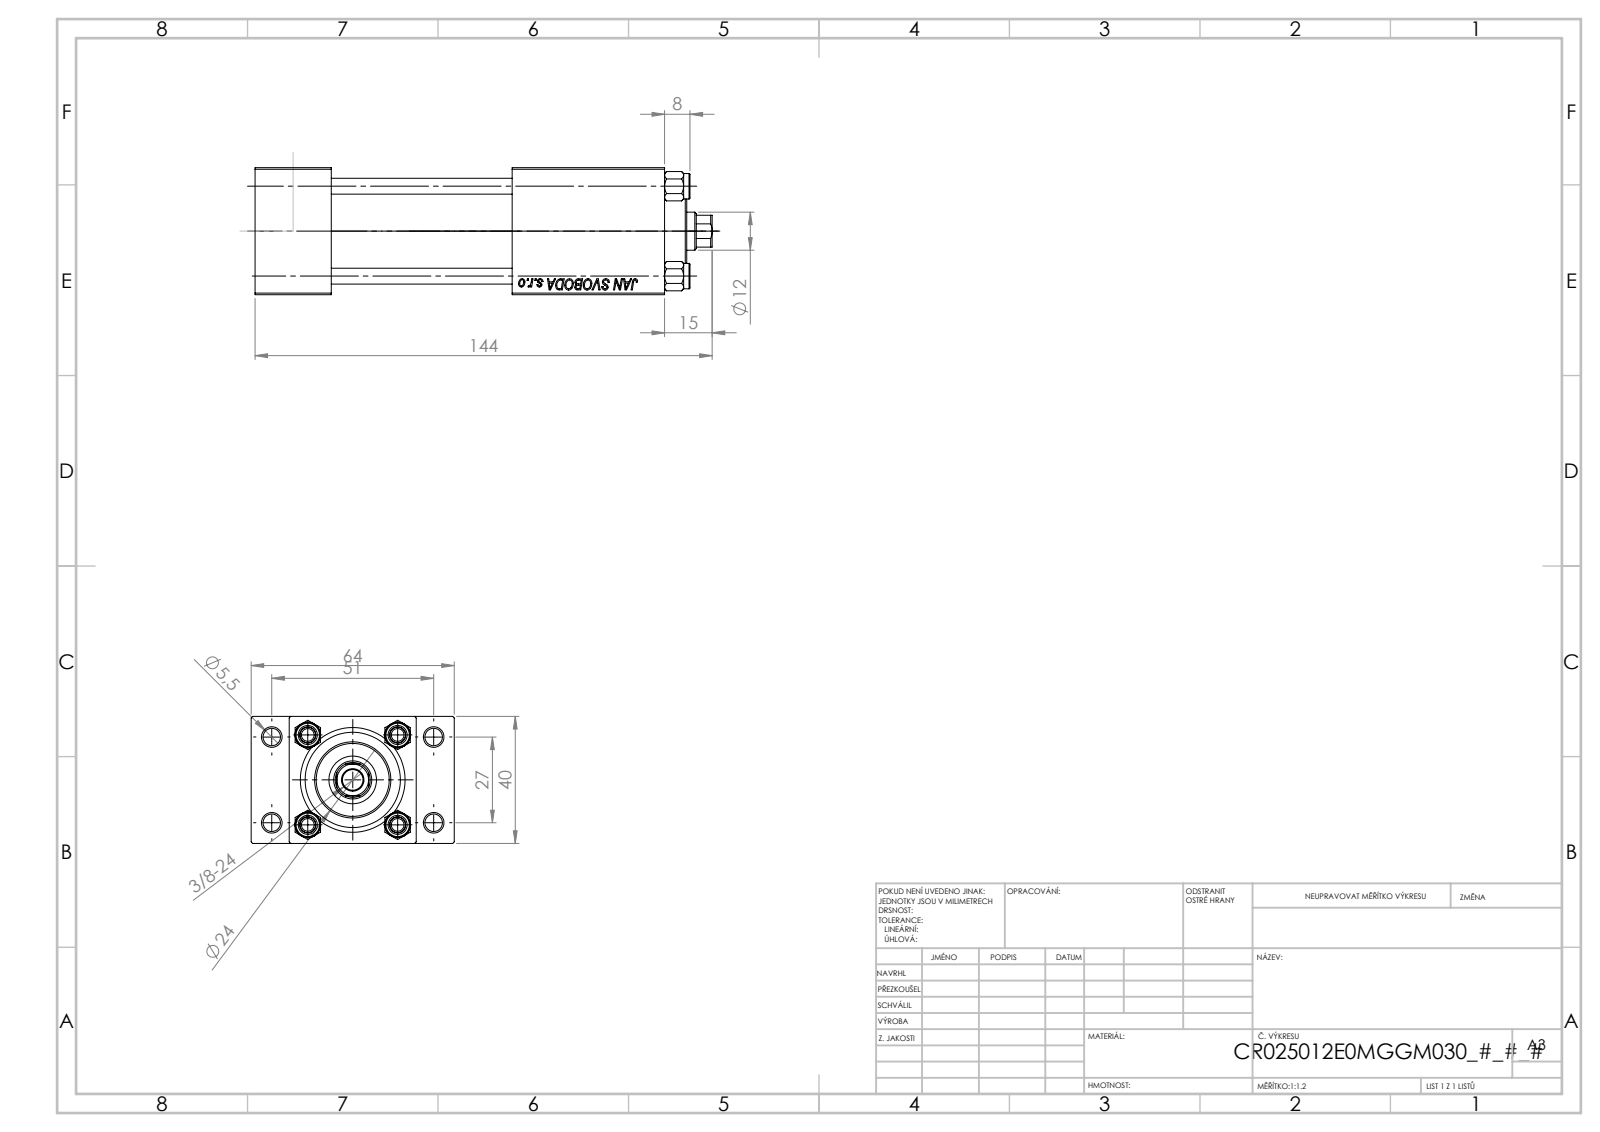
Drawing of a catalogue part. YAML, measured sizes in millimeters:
part_name: "V215CR_E_Body; V215CR_VCP_E; V215CR_TYCINKA_E; NUT_M5_E (+1 more)"
step_written_by: "SolidWorks 2019 (CONFIG_CONTROL_DESIGN)"
units: millimeters
bodies: {solids: 11, faces: 1136, planar: 497, cylindrical: 87, other: 552}
overall_size: [144, 64, 40]
volume: 168470
surface_area: 64869
round_holes:
  - {diameter: 5, count: 4}
  - {diameter: 5.5, count: 4}
  - {diameter: 20, count: 3}
  - {diameter: 7, count: 2}
  - {diameter: 13.16, count: 2}
  - {diameter: 6.5, count: 1}
  - {diameter: 12, count: 1}
  - {diameter: 15, count: 1}
  - {diameter: 25, count: 1}
  - {diameter: 30, count: 1}
round_bosses_or_shafts:
  - {diameter: 8, count: 4}
  - {diameter: 31, count: 1}
  - {diameter: 24, count: 1}
partial_cylinders:
  - {radius: 5.5, count: 1}
face_to_face_distances: [40, 24, 12, 52, 129, 105, 100.3, 76.3, 28.7, 64]
hole_center_spacings: [11.37, 20.01, 28.3, 28.85, 29.89, 39.66, 48.34, 27]
